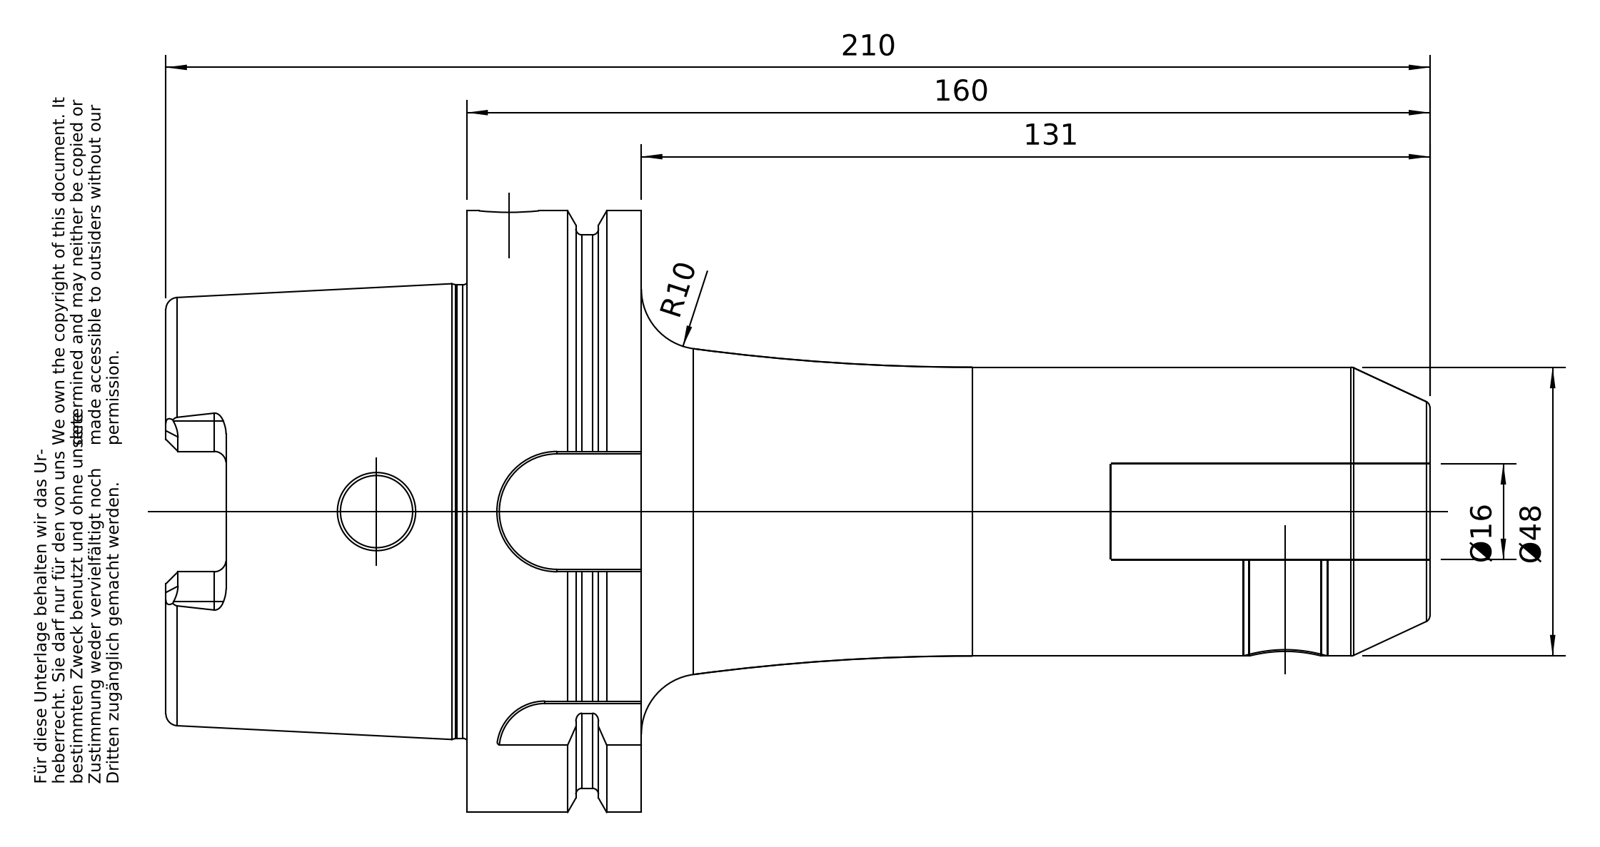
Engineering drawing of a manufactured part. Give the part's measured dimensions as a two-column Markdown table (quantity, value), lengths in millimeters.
| quantity | value |
| --- | --- |
| part name | A100-002-16 |
| STEP written by | PRO/ENGINEER BY PARAMETRIC TECHNOLOGY CORPORATION, 2010430 (CONFIG_CONTROL_DESIGN) |
| units | millimeters |
| bodies | 1 solid, 182 faces (50 planar, 55 cylindrical, 77 other) |
| overall size | 210 × 100 × 100 |
| volume | 488 928 mm³ |
| surface area | 72 263 mm² |
| round holes (diameter × count) | 12 × 2, 10 × 1, 14 × 1, 16 × 1, 22.5 × 1, 24 × 1, 24.32 × 1, 24.5 × 1, 53 × 1, 63 × 1 |
| round bosses / shafts (diameter × count) | 100 × 1, 92 × 1, 75.36 × 1, 48 × 1 |
| partial cylindrical surfaces (radius × count) | 2 × 6, 5 × 4, 8 × 1, 10 × 1, 11 × 1 |
| main face-to-face distances | 29, 12.5, 16.5, 50, 62.5, 79, 210, 160, 147.5, 131 |
| hole center spacings | 129 |
